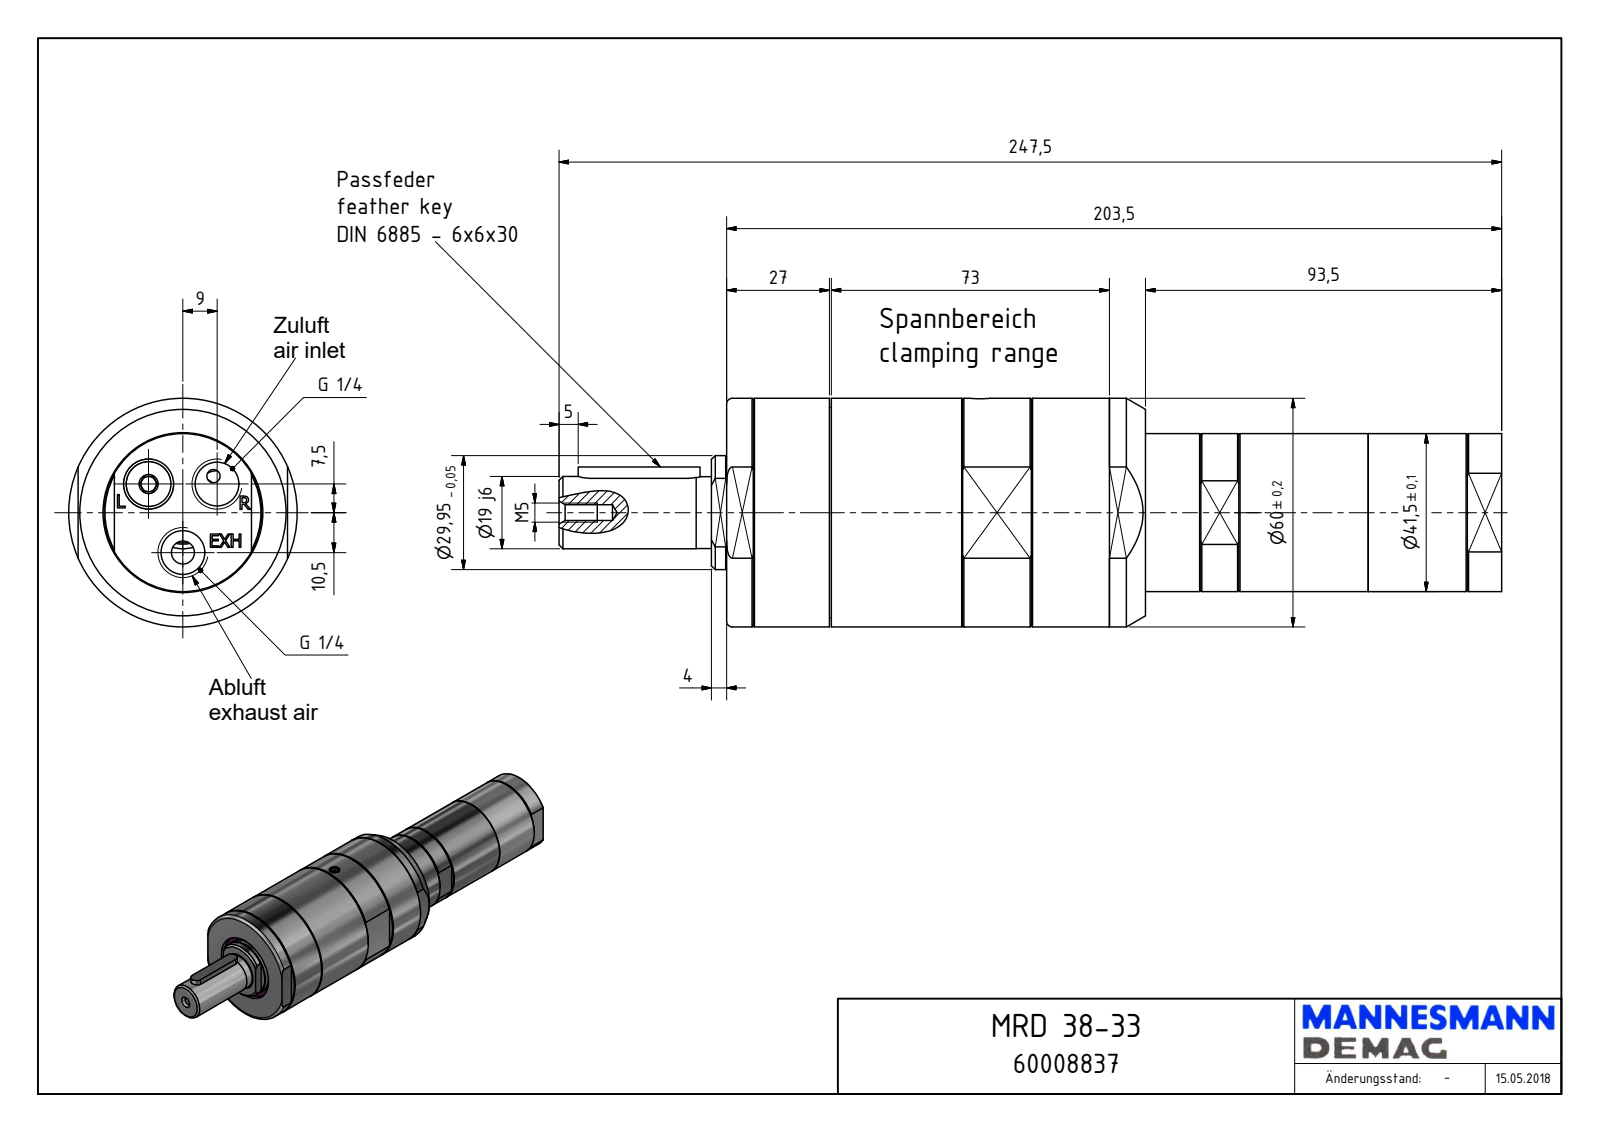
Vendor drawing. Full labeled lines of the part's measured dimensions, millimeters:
Part name (STEP PRODUCT): MRD 38-33_60008837
STEP written by: Autodesk Inventor 2018 (AUTOMOTIVE_DESIGN)
Units: millimetres
Bodies: 1 solid, 500 faces (217 planar, 233 cylindrical, 50 other)
Overall size (bounding box): 247.5 × 60 × 60
Volume: 442 564 mm³ · Surface area: 48 941 mm²
Round holes (diameter × count): ⌀11.45 ×3, ⌀4 ×2, ⌀1.55 ×1, ⌀4.13 ×1, ⌀5.5 ×1, ⌀35 ×1, ⌀42 ×1, ⌀55.38 ×1
Round bosses / shafts (diameter × count): ⌀60 ×1, ⌀55.18 ×1, ⌀41.5 ×1, ⌀38.85 ×1, ⌀29.95 ×1, ⌀19 ×1, ⌀18.8 ×1, ⌀5 ×1
Partial cylindrical surfaces — rounded edges, fillets, slot ends (radius × count): R11.68 ×94, R3 ×2, R24.47 ×1, R24.96 ×1
Main face-to-face distances: 93.5, 203.5, 110, 55, 1, 9.5, 27.5, 82.5, 176, 31
Hole centre spacings: 11.72, 20.12, 10.5, 18
